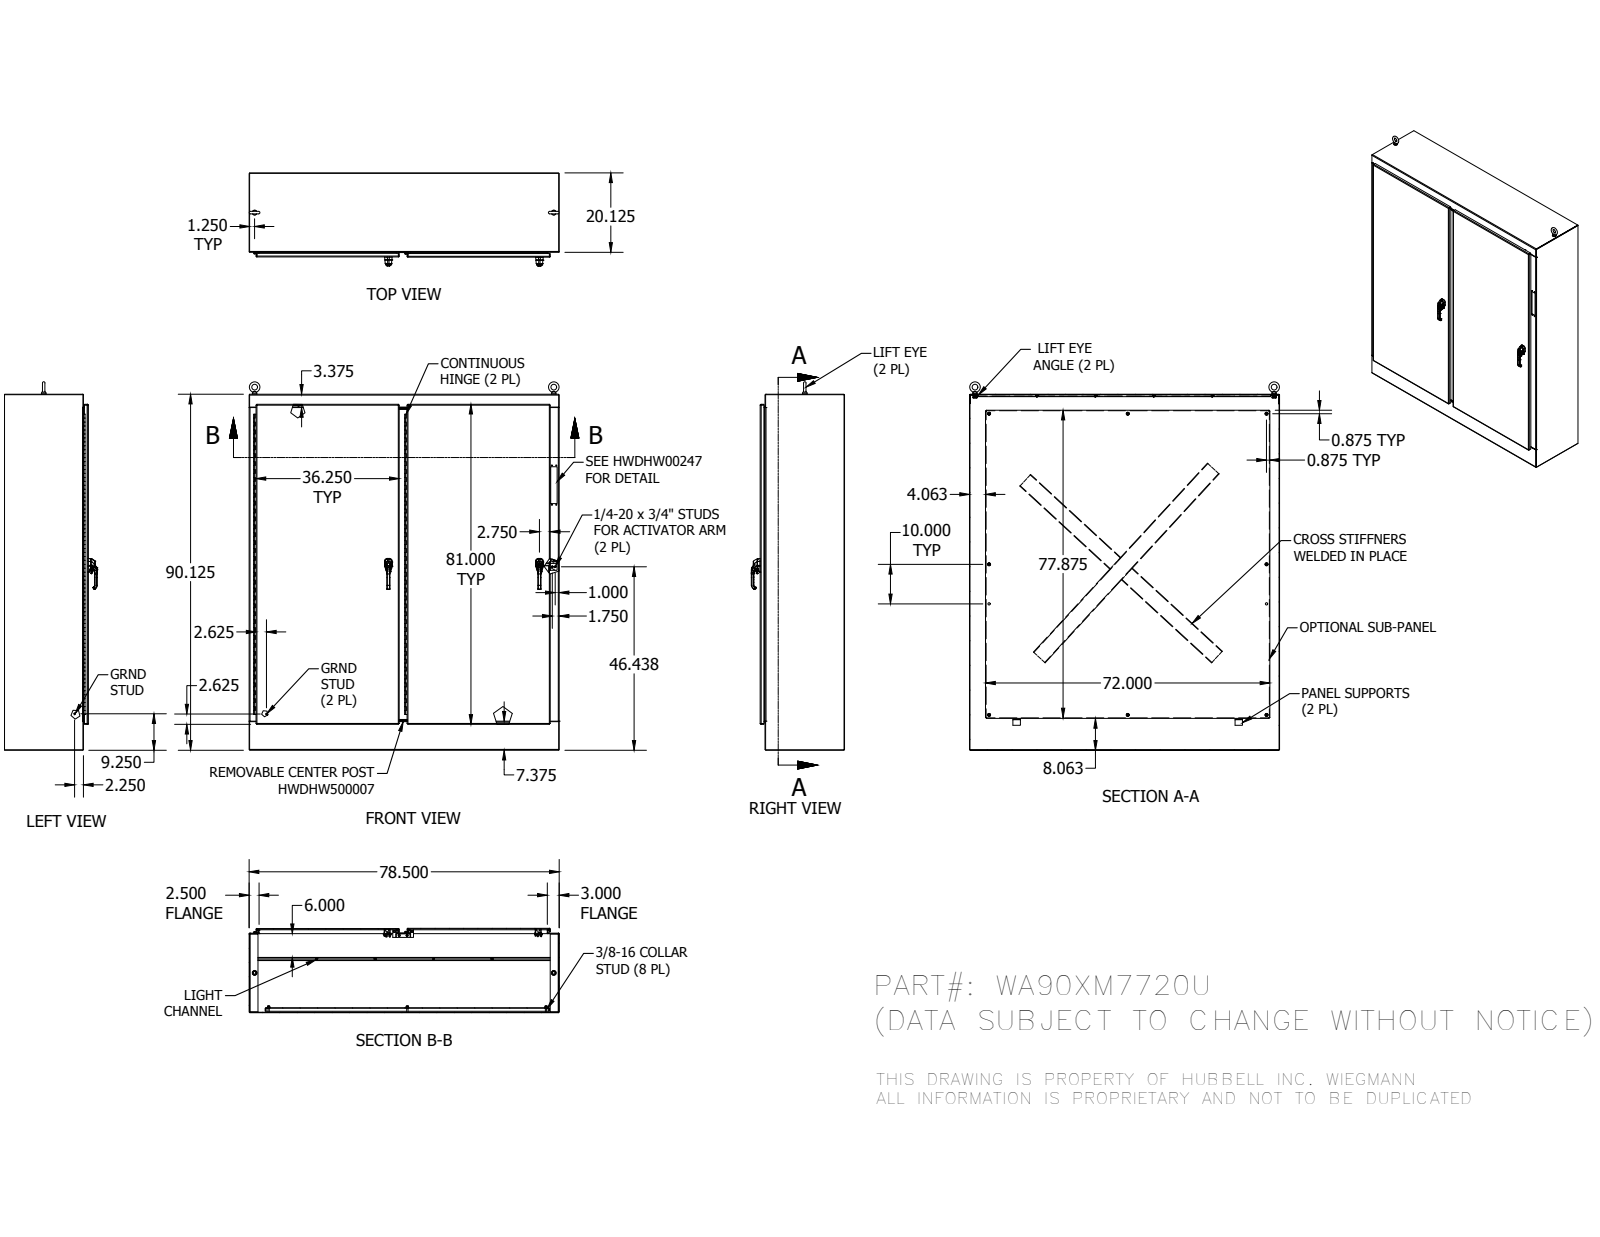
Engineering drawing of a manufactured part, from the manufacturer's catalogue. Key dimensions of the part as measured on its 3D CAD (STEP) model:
Part name (STEP PRODUCT): WA90XM77U_BACK; 3889; 349104; HFW3878 (+8 more)
STEP written by: Autodesk Inventor 2014 (AUTOMOTIVE_DESIGN)
Units: millimetres
Bodies: 226 solids, 9108 faces (4310 planar, 2970 cylindrical, 1828 other)
Overall size (bounding box): 2368.49 × 1993.9 × 599.53
Volume: 49 060 000 mm³ · Surface area: 31 690 000 mm²
Round holes (diameter × count): ⌀6.35 ×18, ⌀9.52 ×18, ⌀7.02 ×16, ⌀7.14 ×10, ⌀4.83 ×8, ⌀5.08 ×8, ⌀7.33 ×8, ⌀7.8 ×8, ⌀7.94 ×8, ⌀8.51 ×8, ⌀9.65 ×8, ⌀3.96 ×6
Round bosses / shafts (diameter × count): ⌀6.35 ×19, ⌀8.38 ×18, ⌀15.88 ×13, ⌀9.52 ×12, ⌀8.56 ×12, ⌀14.29 ×9, ⌀7.11 ×8, ⌀25.4 ×7
Partial cylindrical surfaces — rounded edges, fillets, slot ends (radius × count): R0.5 ×357, R0.3 ×214, R0.51 ×192, R0.47 ×42, R1.27 ×32, R2 ×28, R1.59 ×25, R1.5 ×23
Main face-to-face distances: 3.17, 3.18, 1.59, 4.77, 31.23, 539.23, 536.06, 537.64, 534.47, 540.82
Hole centre spacings: 1828.48, 1847.53, 1.59, 1838.01, 1857.05, 9.66, 40.66, 86.37
